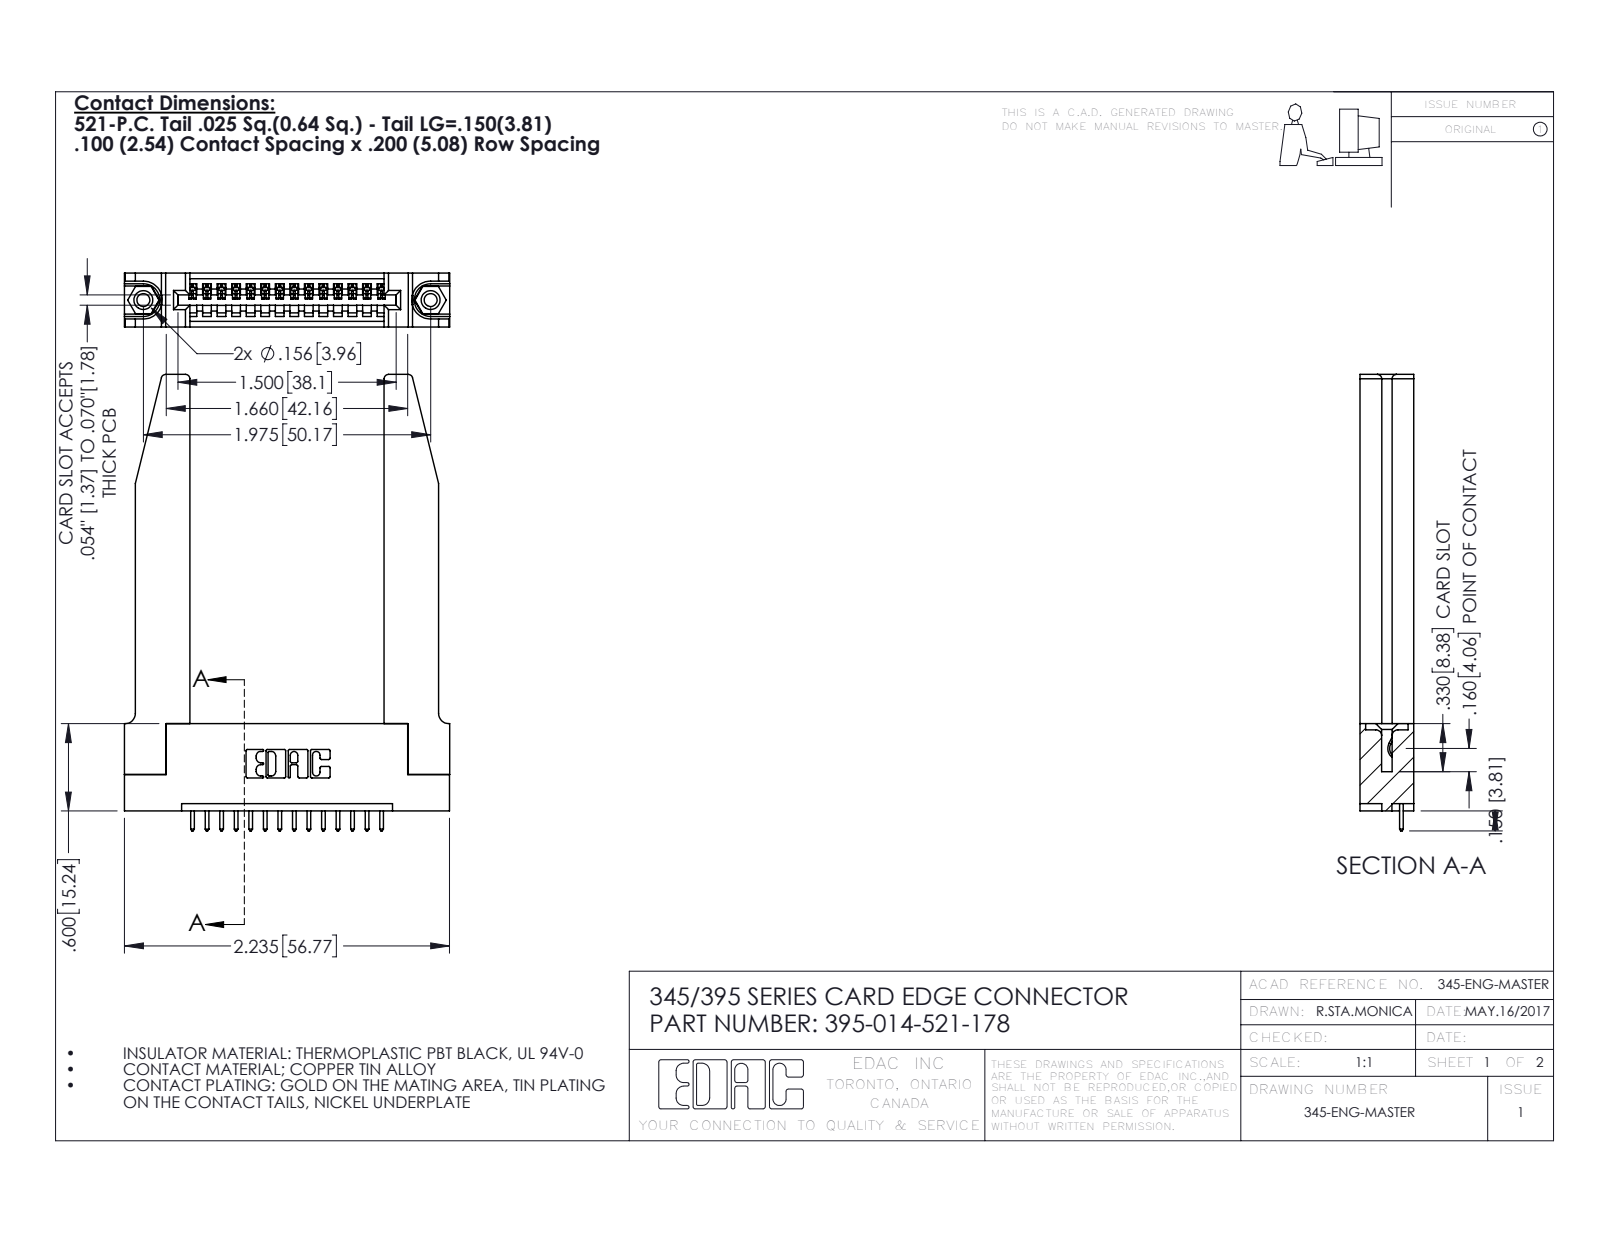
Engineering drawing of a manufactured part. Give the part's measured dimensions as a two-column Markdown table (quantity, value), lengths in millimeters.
| quantity | value |
| --- | --- |
| part name | 345-292-001_345-293-121; 395-014-521-178; 345 Part_Flush Mounting Lugs - 0.156 Dia-TH; 345-220-078_345-220-078 (+1 more) |
| STEP written by | SolidWorks 2016 (CONFIG_CONTROL_DESIGN) |
| units | millimeters |
| bodies | 19 solids, 1172 faces (782 planar, 338 cylindrical, 52 other) |
| overall size | 79.7 × 56.8 × 9.4 |
| volume | 12 900 mm³ |
| surface area | 13 120 mm² |
| round holes (diameter × count) | 2.3 × 2, 3.2 × 2, 4 × 2, 1.6 × 1 |
| round bosses / shafts (diameter × count) | 3.9 × 2 |
| partial cylindrical surfaces (radius × count) | 0.2 × 28, 0.3 × 28, 0.3 × 22, 0.8 × 8, 0.2 × 6, 0.8 × 6, 0.7 × 3, 0.8 × 2 |
| main face-to-face distances | 9.4, 1.8, 7.6, 5.1, 3.8, 3.8, 2, 5.6, 33.9, 2.5 |
| hole center spacings | 6.9, 44.2, 50.2 |
